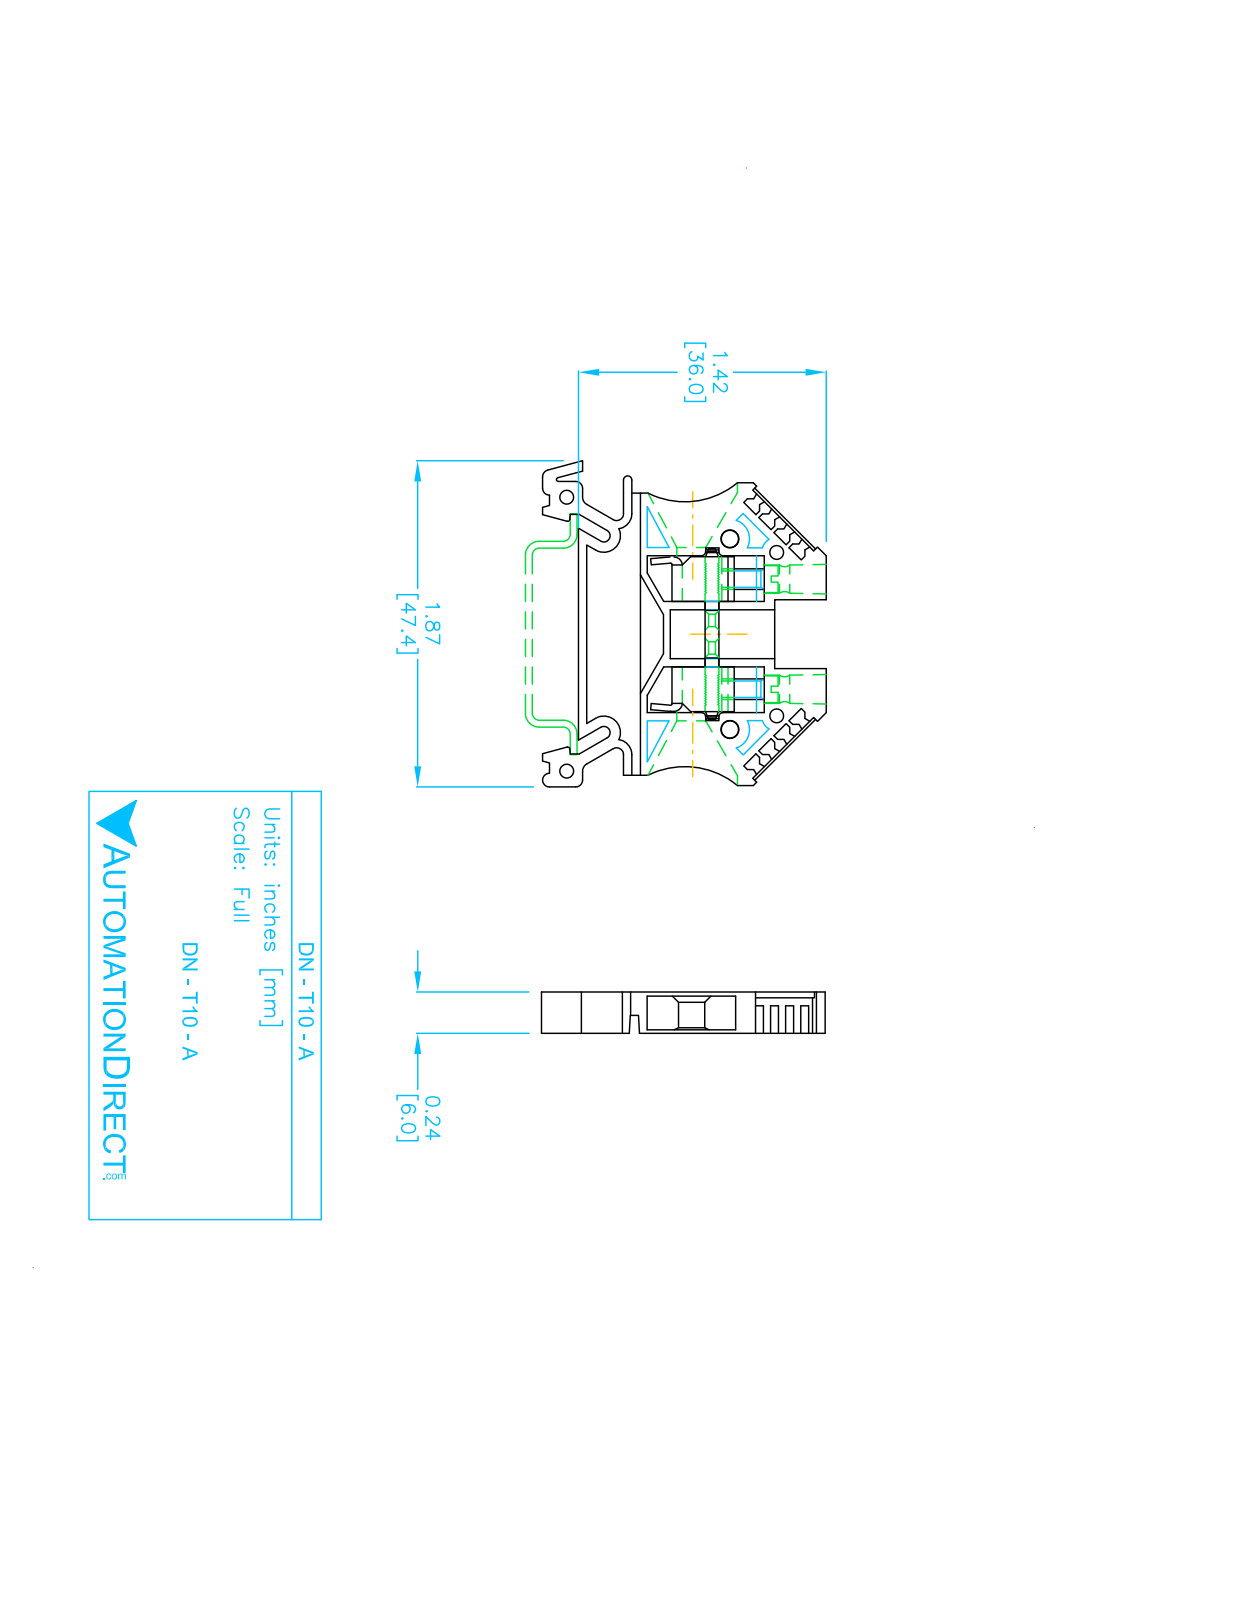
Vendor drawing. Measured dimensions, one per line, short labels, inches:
name: 43409_DN-T10-A
written by: SolidWorks 2013 (AUTOMOTIVE_DESIGN)
unit: in
bodies: 1 solid, 181 faces (141 planar, 40 cylindrical, 0 other)
size: 1.866 × 1.622 × 0.236
volume: 0.381 in³; area: 7.683 in²
holes: 2× ⌀0.079, 2× ⌀0.172
rounds: 7× R0.039, 2× R0.012, 2× R0.035, 2× R0.047, 2× R0.087, 2× R0.094, 2× R0.472, 1× R0.011
face distances: 0.228, 0.236, 0.142, 0.094, 0.047, 0.087, 0.134, 0.354, 0.071, 0.307
hole spacings: 0.63, 1.567
